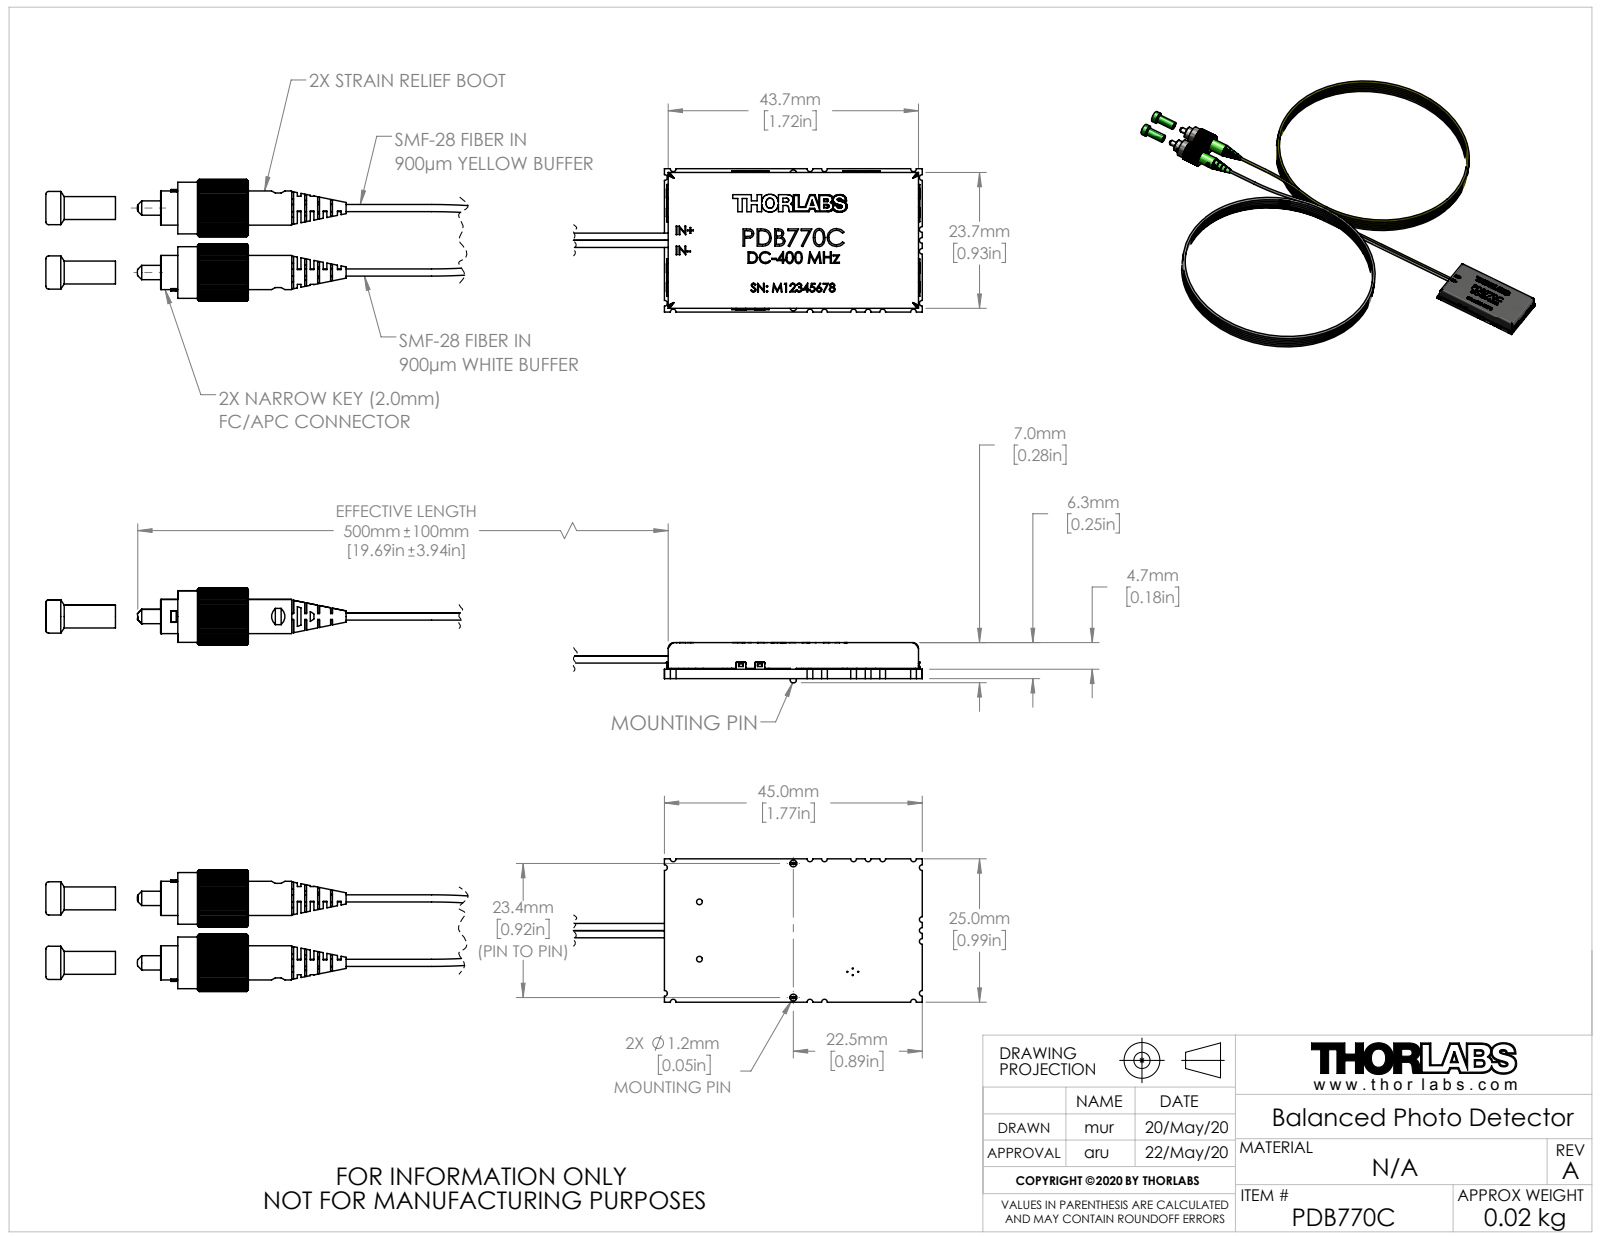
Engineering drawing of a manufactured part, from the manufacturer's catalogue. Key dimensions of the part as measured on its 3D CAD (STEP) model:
Part name (STEP PRODUCT): 20.08.03_PDB770C_WEB
STEP written by: SolidWorks 2018 (AUTOMOTIVE_DESIGN)
Units: millimetres
Bodies: 35 solids, 3216 faces (2408 planar, 589 cylindrical, 219 other)
Overall size (bounding box): 227.81 × 202.5 × 16.55
Volume: 9 451 mm³ · Surface area: 27 717 mm²
Round holes (diameter × count): ⌀0.2 ×4, ⌀1 ×2, ⌀1.2 ×2, ⌀1.4 ×2, ⌀2.65 ×2, ⌀3.01 ×2, ⌀3.05 ×2, ⌀3.94 ×2, ⌀4.44 ×2, ⌀5.08 ×2, ⌀8.25 ×2, ⌀9.02 ×2
Round bosses / shafts (diameter × count): ⌀1.25 ×6, ⌀0.25 ×3, ⌀7.11 ×2, ⌀5.97 ×2, ⌀5.8 ×2, ⌀4.95 ×2, ⌀4 ×2, ⌀3.81 ×2
Partial cylindrical surfaces — rounded edges, fillets, slot ends (radius × count): R0.15 ×80, R0.3 ×18, R0.5 ×18, R0.28 ×12, R0.38 ×11, R0.15 ×8, R0.4 ×7, R0.7 ×4
Main face-to-face distances: 1.64, 6.29, 4.65, 5.99, 4.35, 23.41, 0.96, 23.71, 23.11, 3.24
Hole centre spacings: 1.11, 9.15, 9.6, 17.72, 23.41, 0.75, 1.15, 1.9
